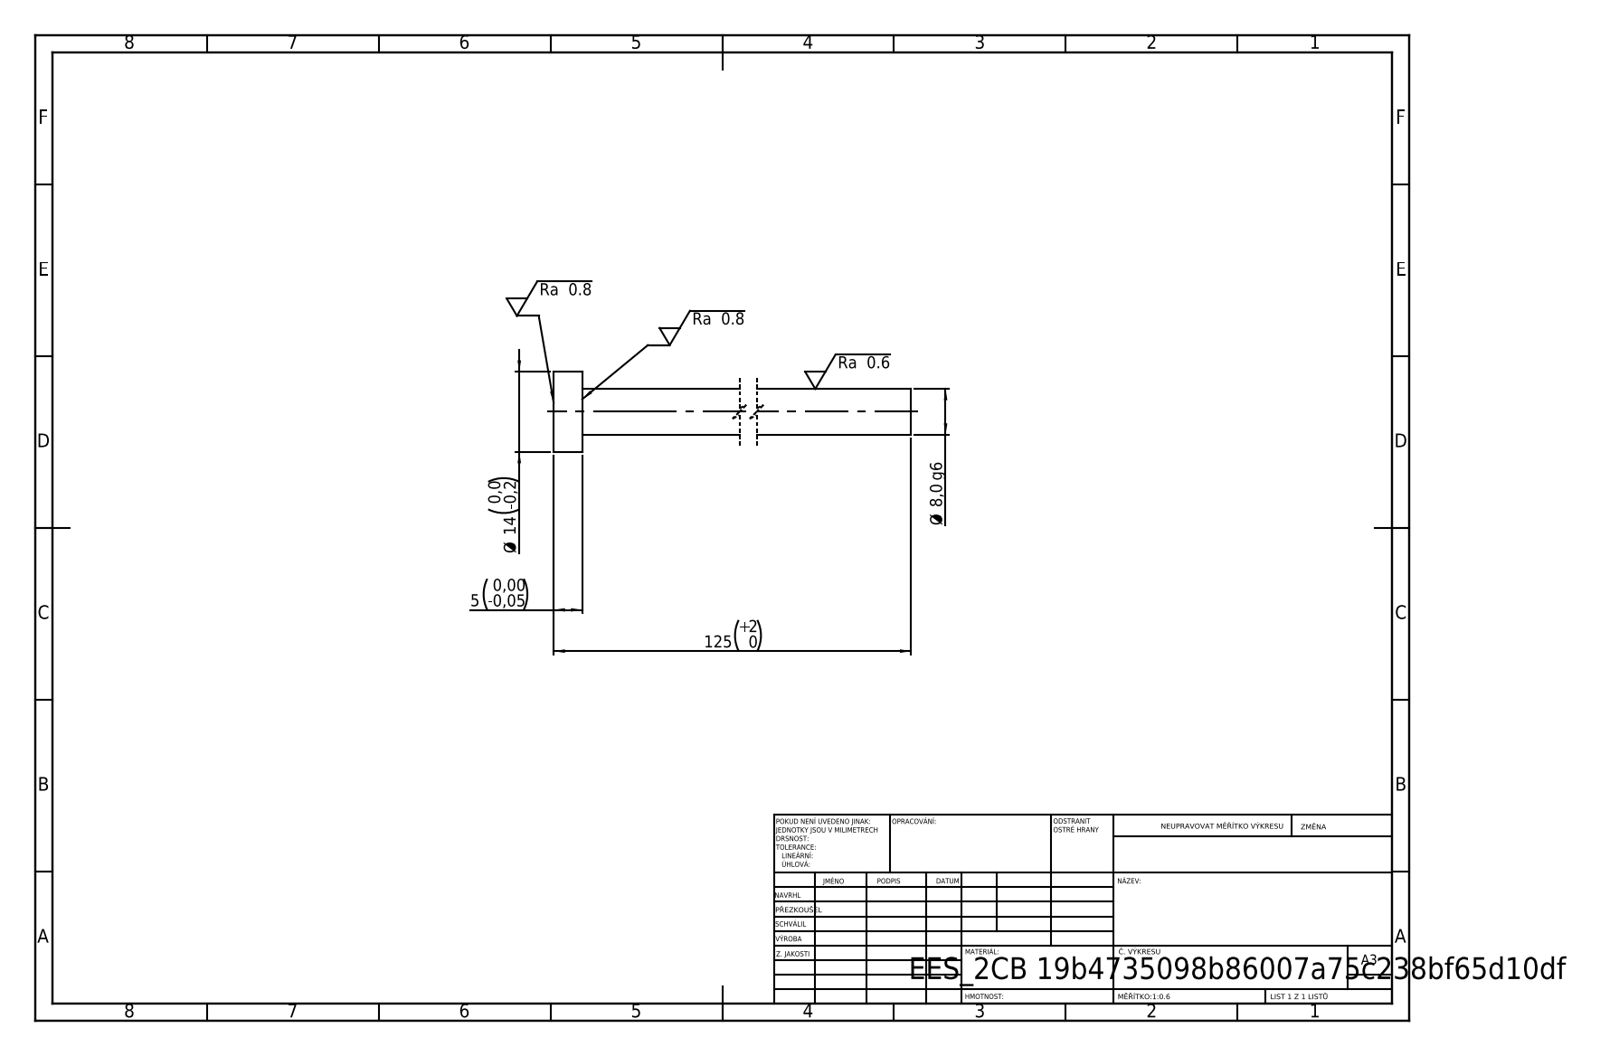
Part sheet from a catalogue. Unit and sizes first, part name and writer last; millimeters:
Units: millimetres
Overall size (bounding box): 125 × 14 × 14
Round bosses / shafts (diameter × count): ⌀14 ×1, ⌀8 ×1
Main face-to-face distances: 5, 125, 120
Volume: 6 802 mm³ · Surface area: 3 544 mm²
Bodies: 1 solid, 7 faces (3 planar, 4 cylindrical, 0 other)
STEP written by: SolidWorks 2019 (CONFIG_CONTROL_DESIGN)
